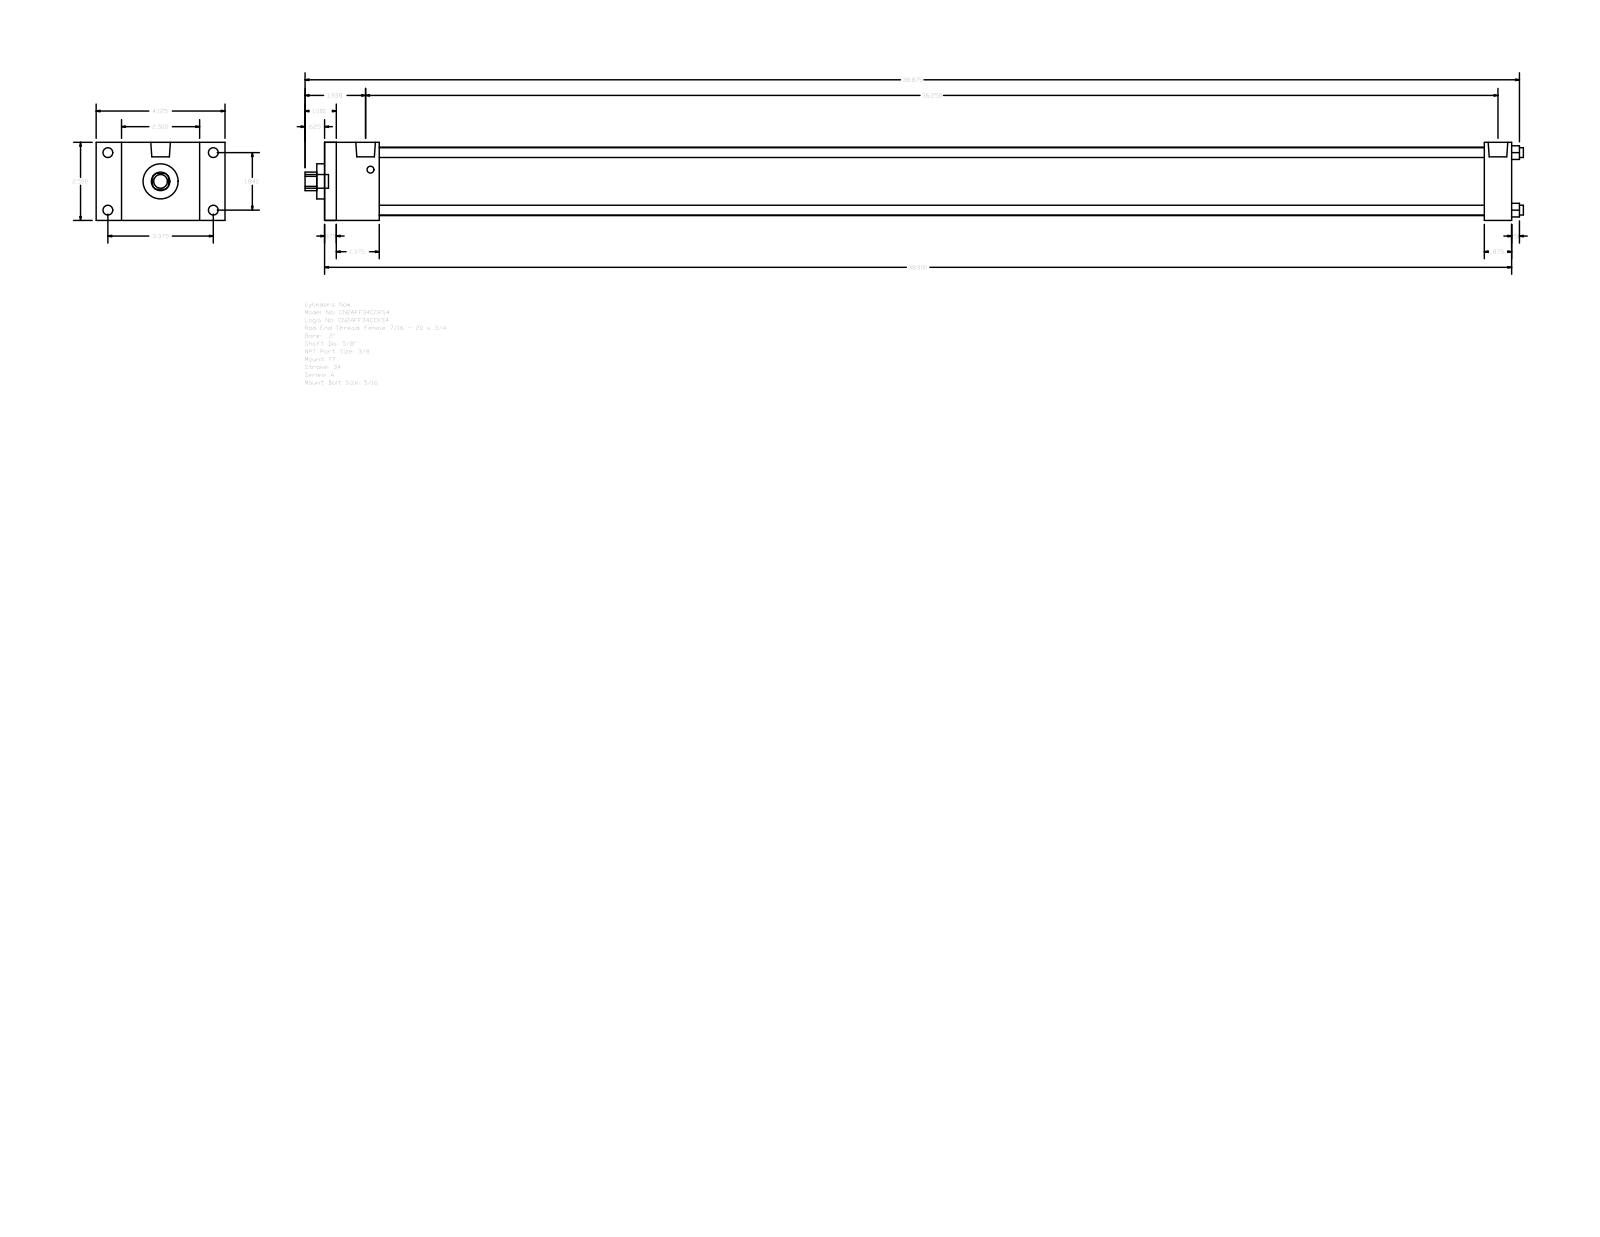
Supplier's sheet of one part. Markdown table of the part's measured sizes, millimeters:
| quantity | value |
| --- | --- |
| part name | A_FF__0200_0.625 |
| STEP written by | GSSL Pune (CONFIG_CONTROL_DESIGN) |
| units | millimeters |
| bodies | 0 solids, 92 faces (64 planar, 28 cylindrical, 0 other) |
| overall size | 990.6 × 104.78 × 63.5 |
| round holes (diameter × count) | 7.94 × 4, 15.88 × 1, 28.57 × 1, 55.63 × 1 |
| round bosses / shafts (diameter × count) | 7.94 × 4, 5.56 × 4, 15.93 × 2, 11.11 × 1 |
| partial cylindrical surfaces (radius × count) | 7.54 × 1 |
| main face-to-face distances | 63.5, 965.2, 9.52, 955.68, 44.45, 942.97, 34.93, 933.45, 898.52, 920.75 |
| hole center spacings | 33.05, 46.74, 66.1 |
